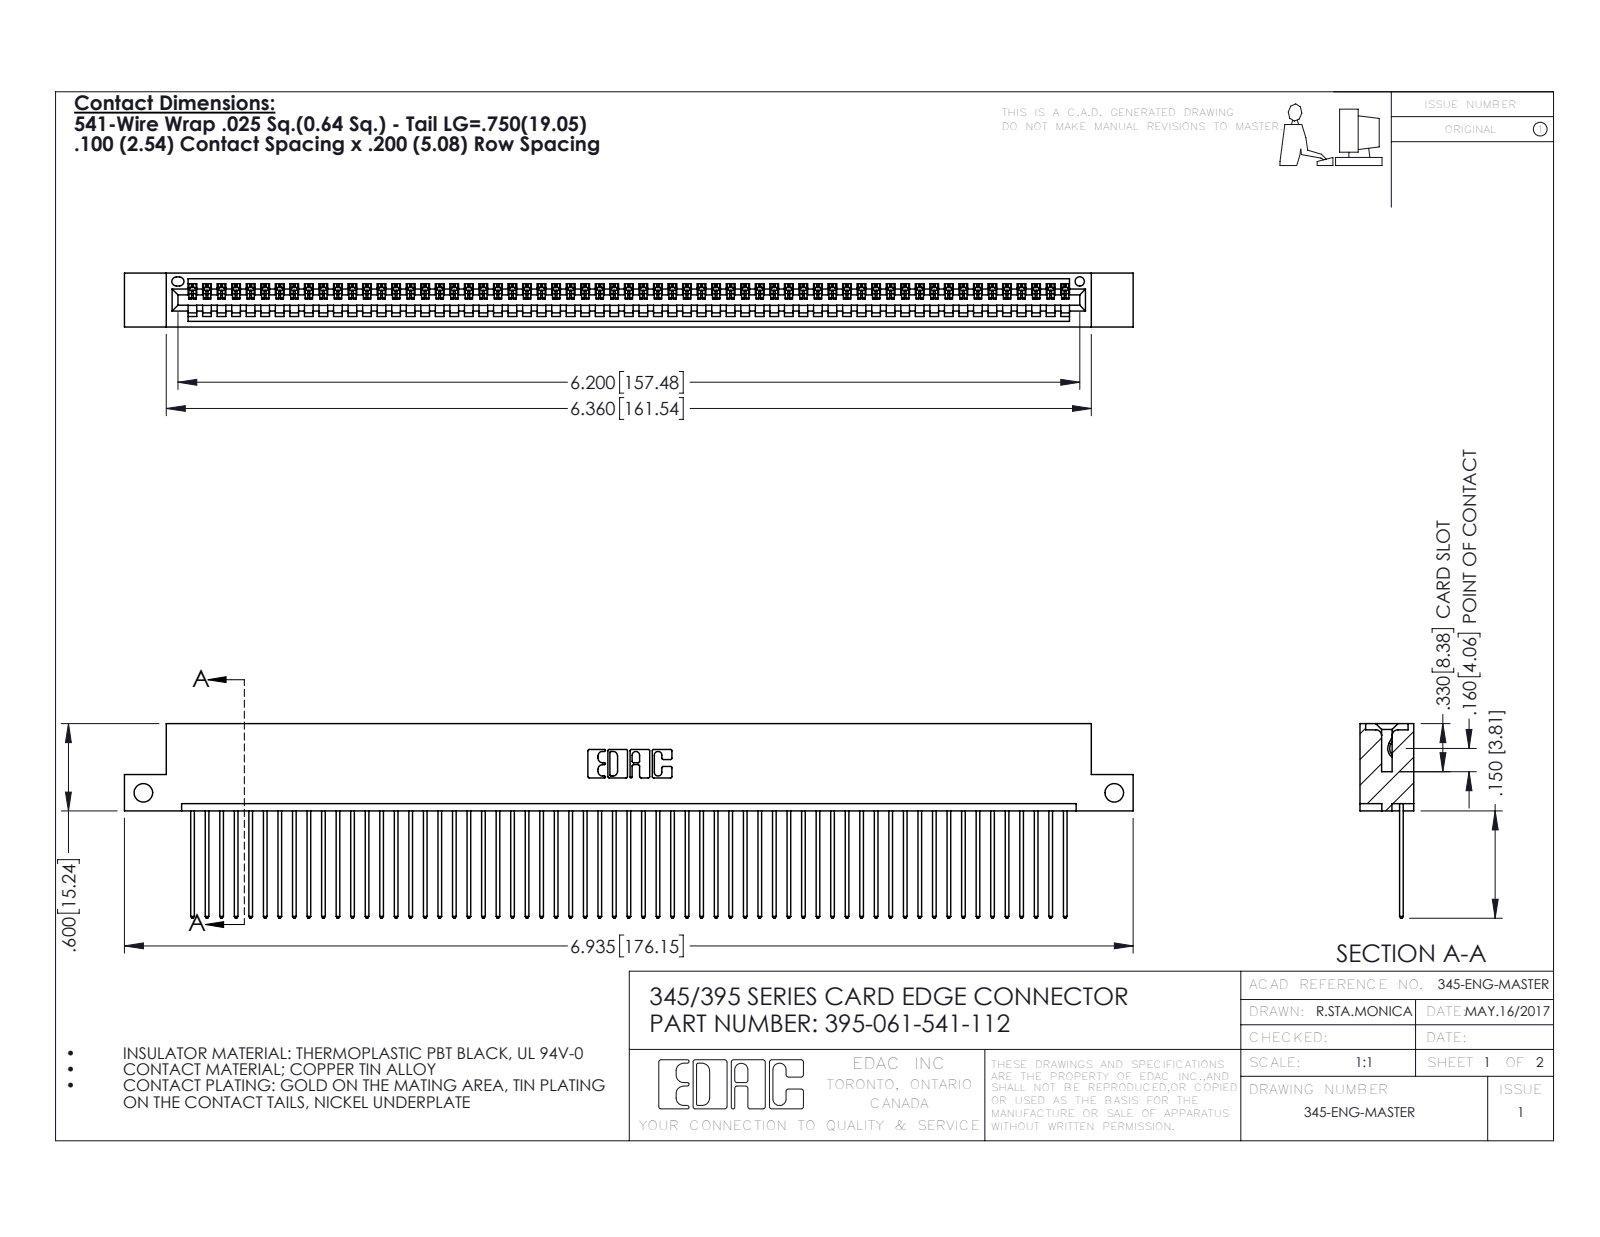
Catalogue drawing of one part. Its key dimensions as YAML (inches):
part_name: "345 Part_Flush Mounting Lugs - Side Mount; 395-061-541-112; 345-292-001_345-293-141"
step_written_by: "SolidWorks 2016 (CONFIG_CONTROL_DESIGN)"
units: inches
bodies: {solids: 62, faces: 3664, planar: 2520, cylindrical: 1144, other: 0}
overall_size: [6.935, 1.337, 0.37]
volume: 1.037
surface_area: 37.03
round_holes:
  - {diameter: 0.128, count: 2}
  - {diameter: 0.064, count: 1}
partial_cylinders:
  - {radius: 0.006, count: 122}
  - {radius: 0.01, count: 122}
  - {radius: 0.01, count: 22}
  - {radius: 0.007, count: 6}
  - {radius: 0.031, count: 6}
  - {radius: 0.026, count: 3}
  - {radius: 0.031, count: 2}
  - {radius: 0.04, count: 2}
face_to_face_distances: [0.072, 0.298, 0.098, 0.272, 0.025, 0.37, 0.2, 0.225, 0.149, 0.072]
hole_center_spacings: [6.675]
